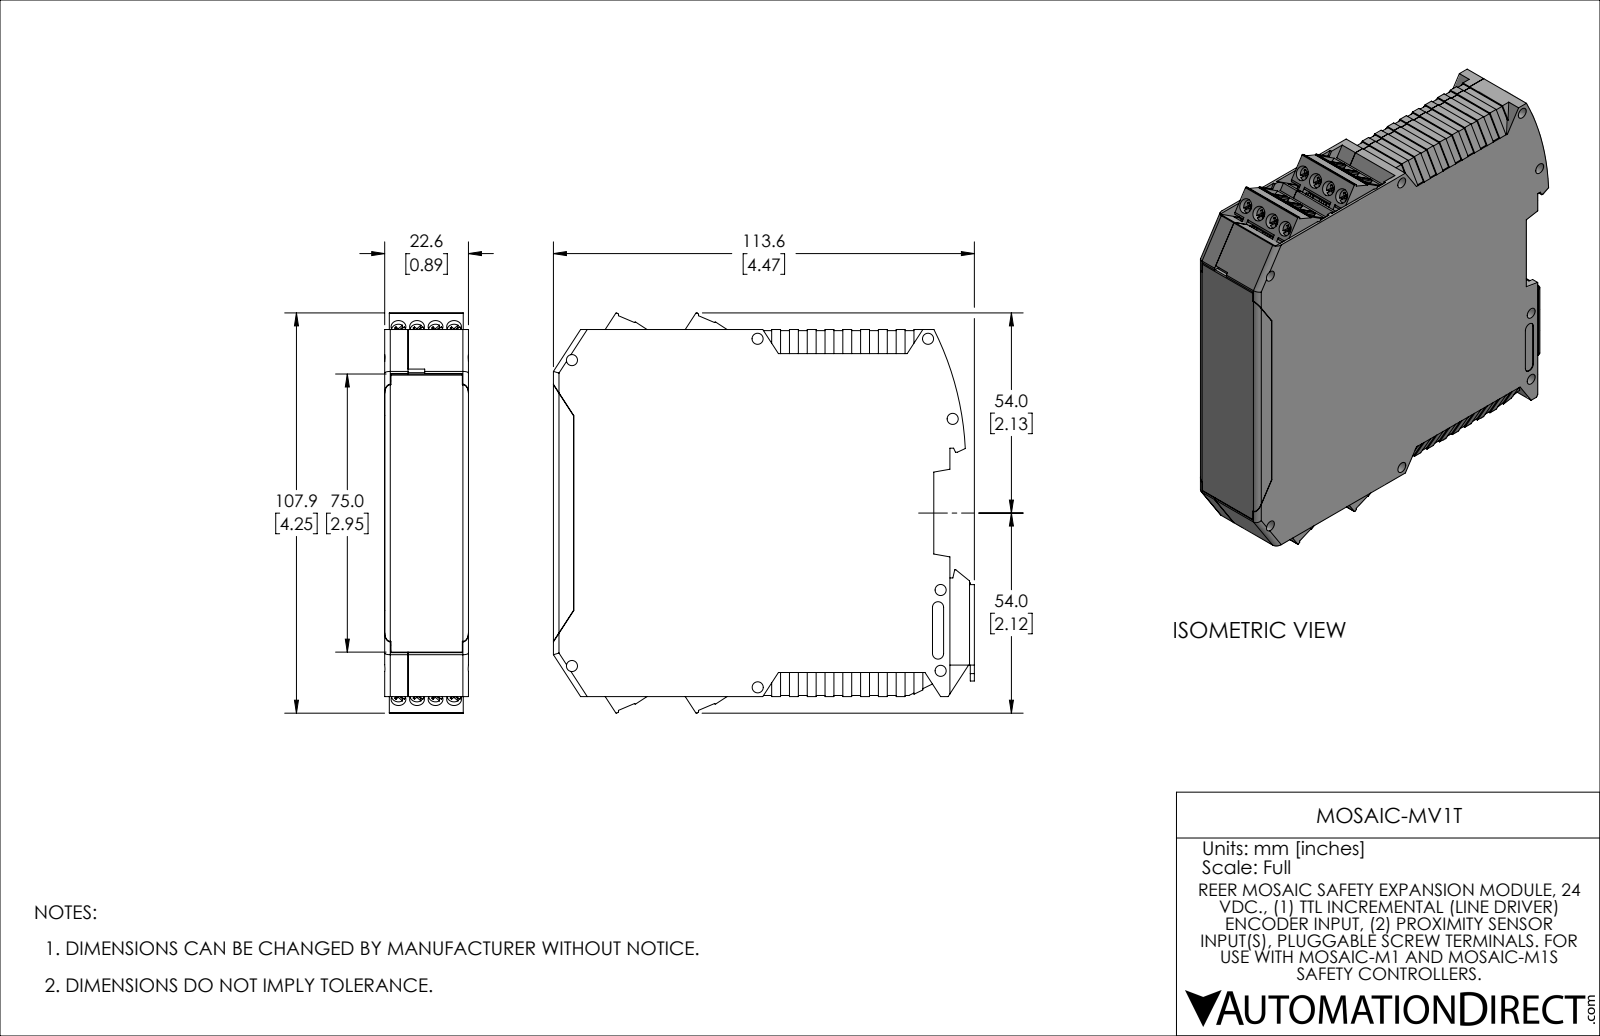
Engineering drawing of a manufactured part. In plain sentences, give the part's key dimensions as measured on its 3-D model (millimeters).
The part is named "MOSAIC-MV1T". Its 3-D file was written by "SolidWorks 2021 (AUTOMOTIVE_DESIGN)". It is 9 solids with 1831 faces: 1569 planar, 259 cylindrical and 3 other. Overall it measures 113.6 by 108 by 22.6 millimeters. Its volume is 57 090 cubic millimeters and its surface area 75 810 square millimeters. Round holes: 18 of diameter 1.4, 16 of diameter 2.8, 16 of diameter 4, 14 of diameter 3, 1 of diameter 1.6. Round bosses or shafts: 16 of diameter 3.8, 1 of diameter 4.5, 1 of diameter 2.8, 1 of diameter 1.3. Partial cylindrical surfaces (rounded edges, fillets, slot ends): 33 of radius 0.3, 16 of radius 2.9, 12 of radius 0.2, 12 of radius 0.8, 8 of radius 1.5, 6 of radius 0.8, 5 of radius 2.5, 4 of radius 0.6. The main face-to-face distances are 1.2, 21.4, 22.6, 20.1, 1, 6.3, 1.2, 5.1, 15.1, 16.3. The hole center spacings are 5, 10, 12.8, 18.8, 11.8, 15, 15.4, 18.1.
